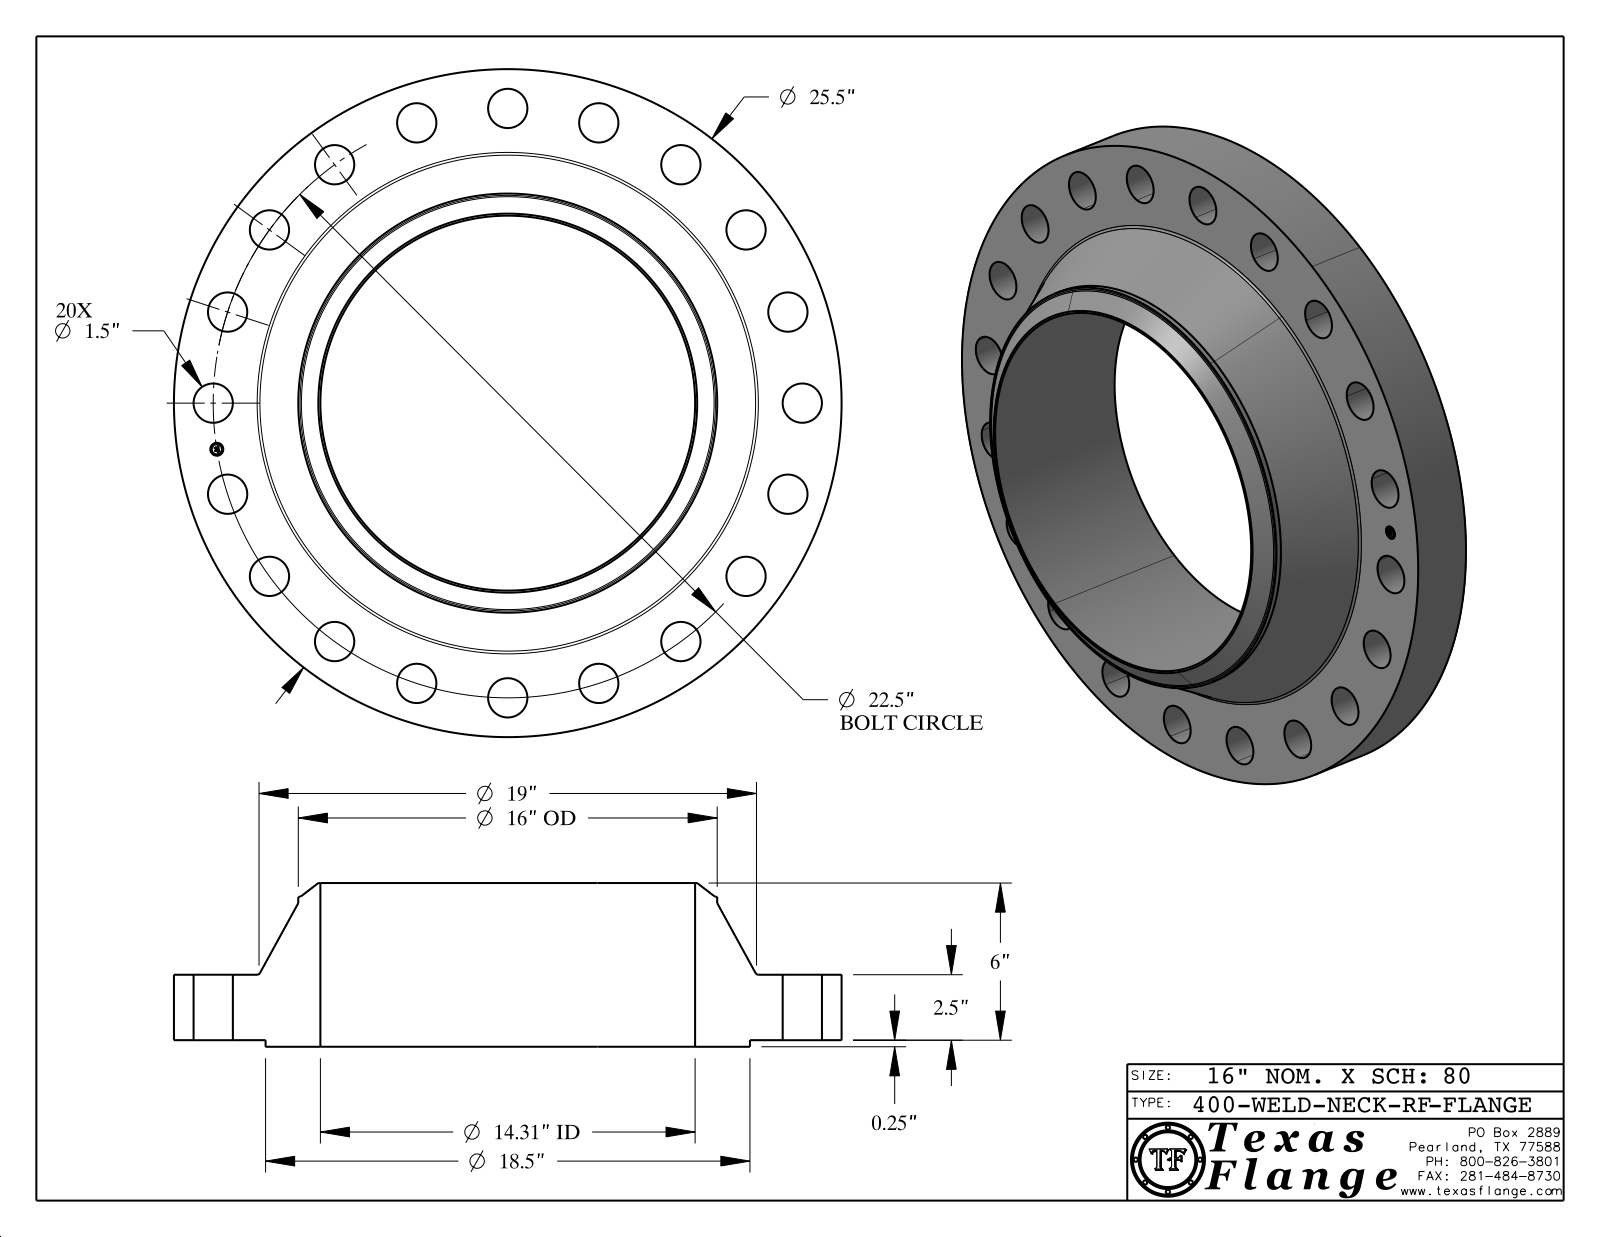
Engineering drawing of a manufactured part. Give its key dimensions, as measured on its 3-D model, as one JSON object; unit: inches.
{"part_name": "400-WELD-NECK-RF", "step_written_by": "CATIA V5 STEP AP214 (AUTOMOTIVE_DESIGN)", "units": "inches", "bodies": {"solids": 1, "faces": 447, "planar": 369, "cylindrical": 68, "other": 10}, "overall_size": [25.5, 25.5, 6.25], "volume_in3": 1053, "surface_area_in2": 1469, "round_holes": [[1.5, 20], [0.495, 1], [14.312, 1]], "round_bosses_or_shafts": [[0.03, 8], [25.5, 1], [18.5, 1], [16, 1], [0.39, 1]], "face_to_face_distances": [2.5, 0.25, 2.75, 6.25, 6, 3.5, 2.735, 2.485, 0.015, 3.515], "hole_center_spacings": [11.25, 6.953, 13.225, 3.52, 18.203, 20.048, 21.399, 22.223]}
